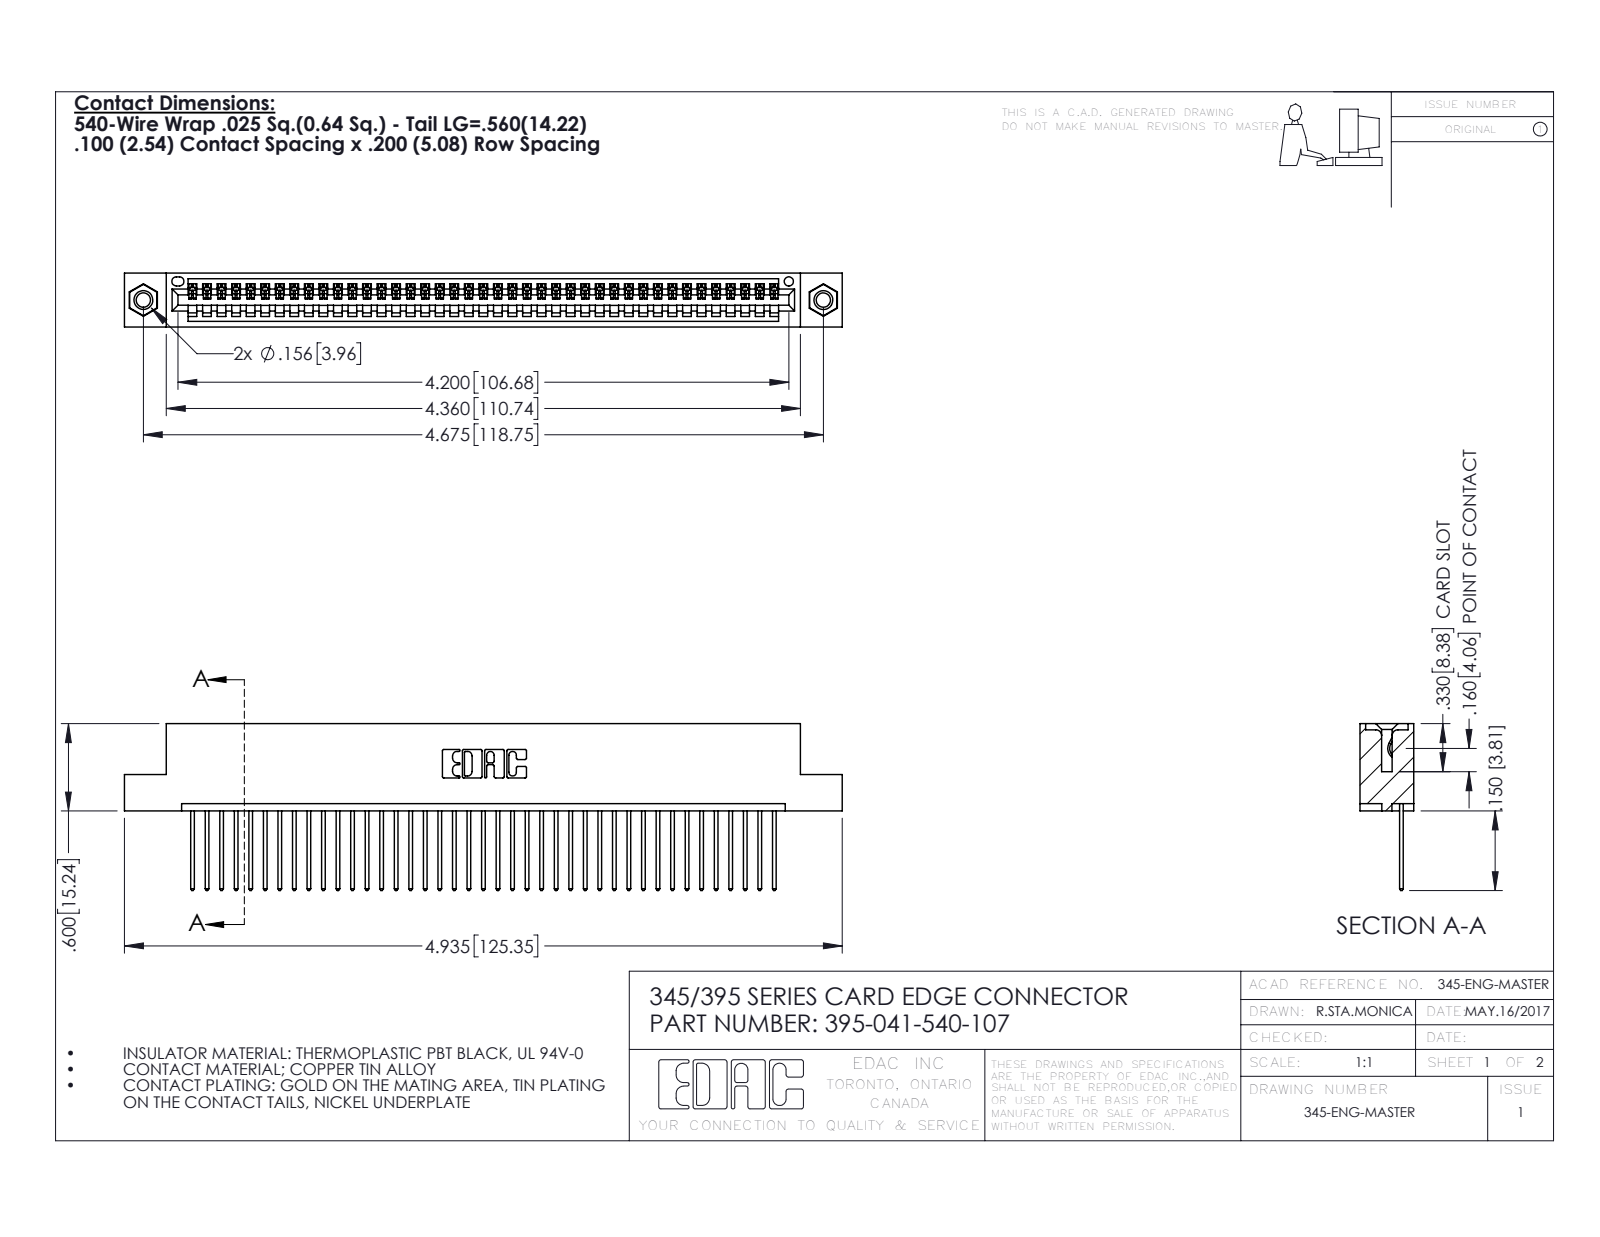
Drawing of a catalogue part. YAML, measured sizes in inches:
part_name: "395-041-540-107; 345-292-001_345-293-140; 345 Part_Flush Mounting Lugs - 0.156 Dia-TI; 345-250-001_345-250-005-103"
step_written_by: "SolidWorks 2016 (CONFIG_CONTROL_DESIGN)"
units: inches
bodies: {solids: 44, faces: 2564, planar: 1752, cylindrical: 796, other: 16}
overall_size: [4.935, 1.147, 0.37]
volume: 0.729
surface_area: 25.24
round_holes:
  - {diameter: 0.098, count: 2}
  - {diameter: 0.125, count: 2}
  - {diameter: 0.156, count: 2}
  - {diameter: 0.064, count: 1}
round_bosses_or_shafts:
  - {diameter: 0.155, count: 2}
partial_cylinders:
  - {radius: 0.006, count: 82}
  - {radius: 0.01, count: 82}
  - {radius: 0.01, count: 22}
  - {radius: 0.007, count: 6}
  - {radius: 0.031, count: 6}
  - {radius: 0.026, count: 3}
  - {radius: 0.031, count: 2}
  - {radius: 0.04, count: 2}
face_to_face_distances: [0.072, 0.298, 0.37, 0.098, 0.272, 0.025, 0.2, 0.225, 0.149, 0.072]
hole_center_spacings: [0.27, 4.439, 4.675]
